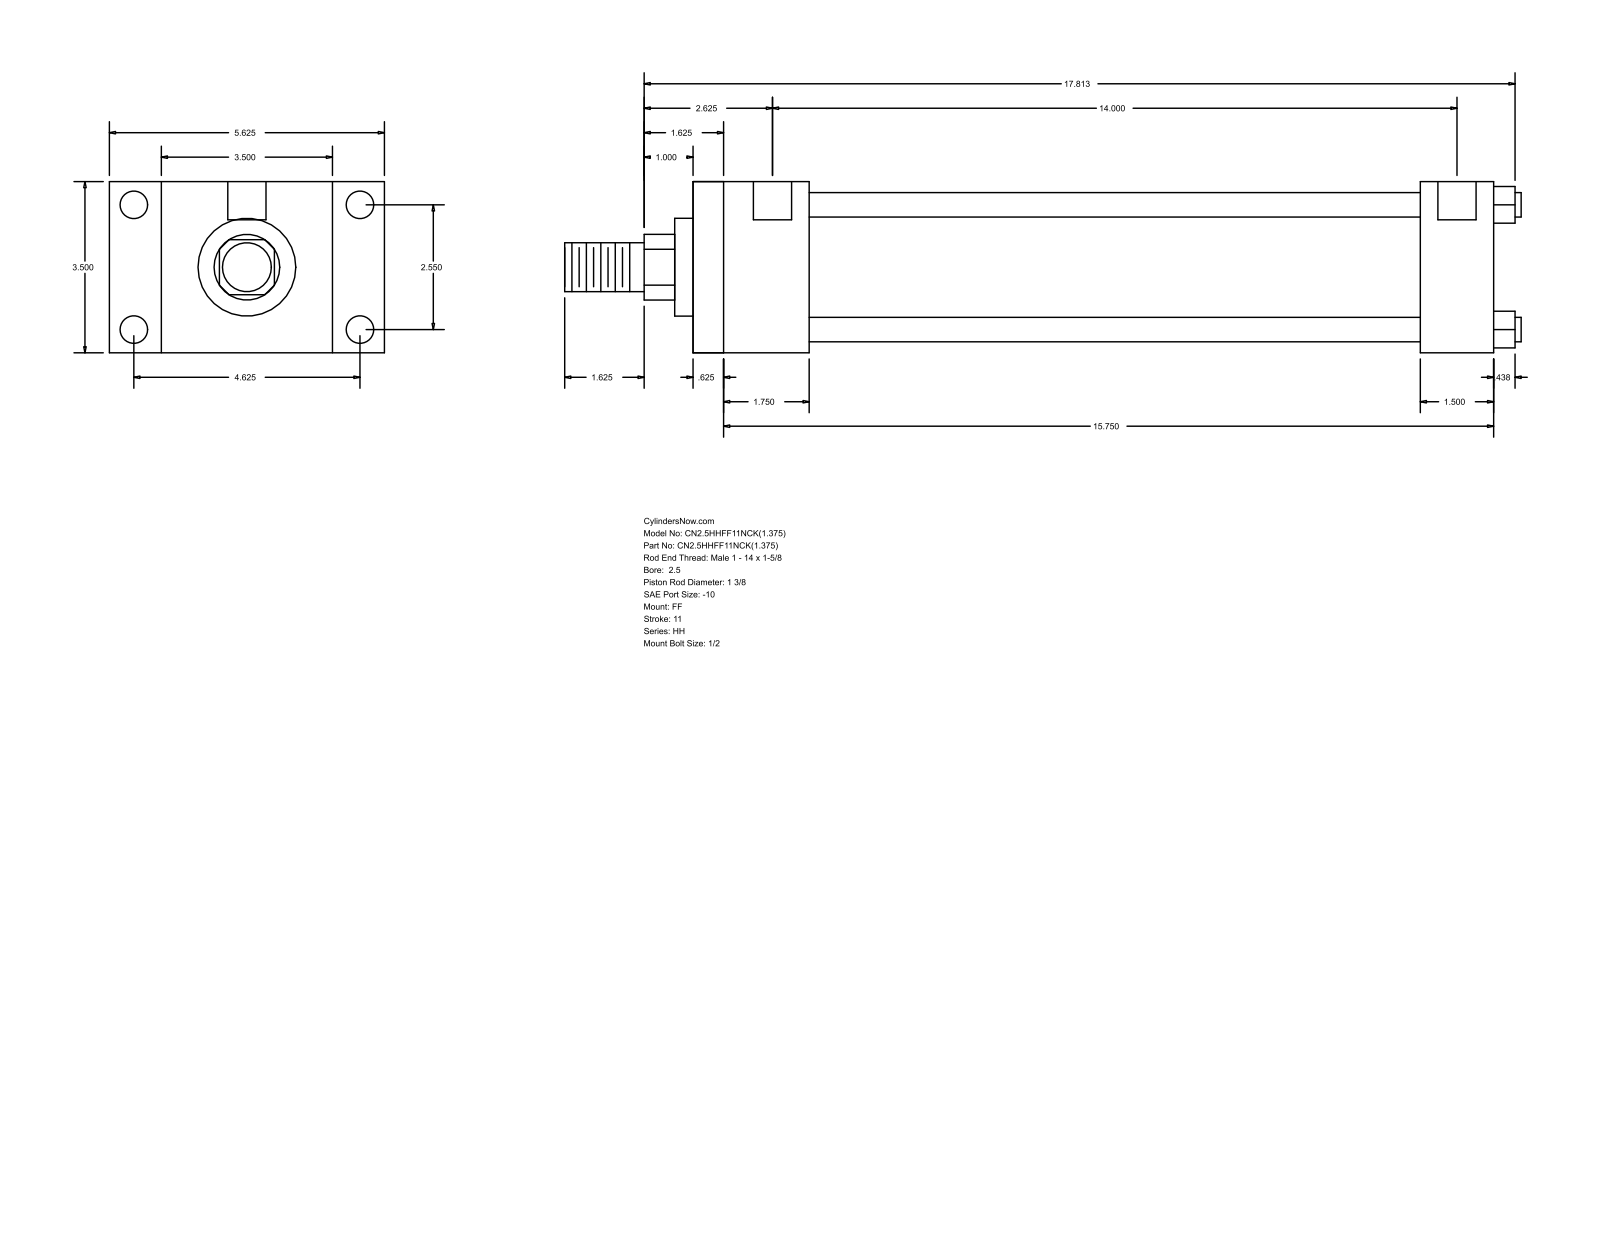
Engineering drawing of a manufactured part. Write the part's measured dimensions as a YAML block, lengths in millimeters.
part_name: "HH_FF__0250_1.375"
step_written_by: "GSSL Pune (CONFIG_CONTROL_DESIGN)"
units: millimeters
bodies: {solids: 0, faces: 92, planar: 64, cylindrical: 28, other: 0}
overall_size: [496.89, 142.88, 88.9]
round_holes:
  - {diameter: 5.56, count: 4}
  - {diameter: 14.3, count: 4}
  - {diameter: 19.84, count: 2}
round_bosses_or_shafts:
  - {diameter: 12.7, count: 4}
  - {diameter: 73.03, count: 1}
  - {diameter: 50.8, count: 1}
  - {diameter: 34.92, count: 1}
  - {diameter: 25.4, count: 1}
partial_cylinders:
  - {radius: 17.06, count: 1}
face_to_face_distances: [88.9, 415.92, 15.87, 400.05, 60.32, 44.45, 355.6, 377.83, 361.96, 317.51]
hole_center_spacings: [64.76, 117.48, 134.15, 358.77, 1.58, 1.59, 355.6, 357.18]
